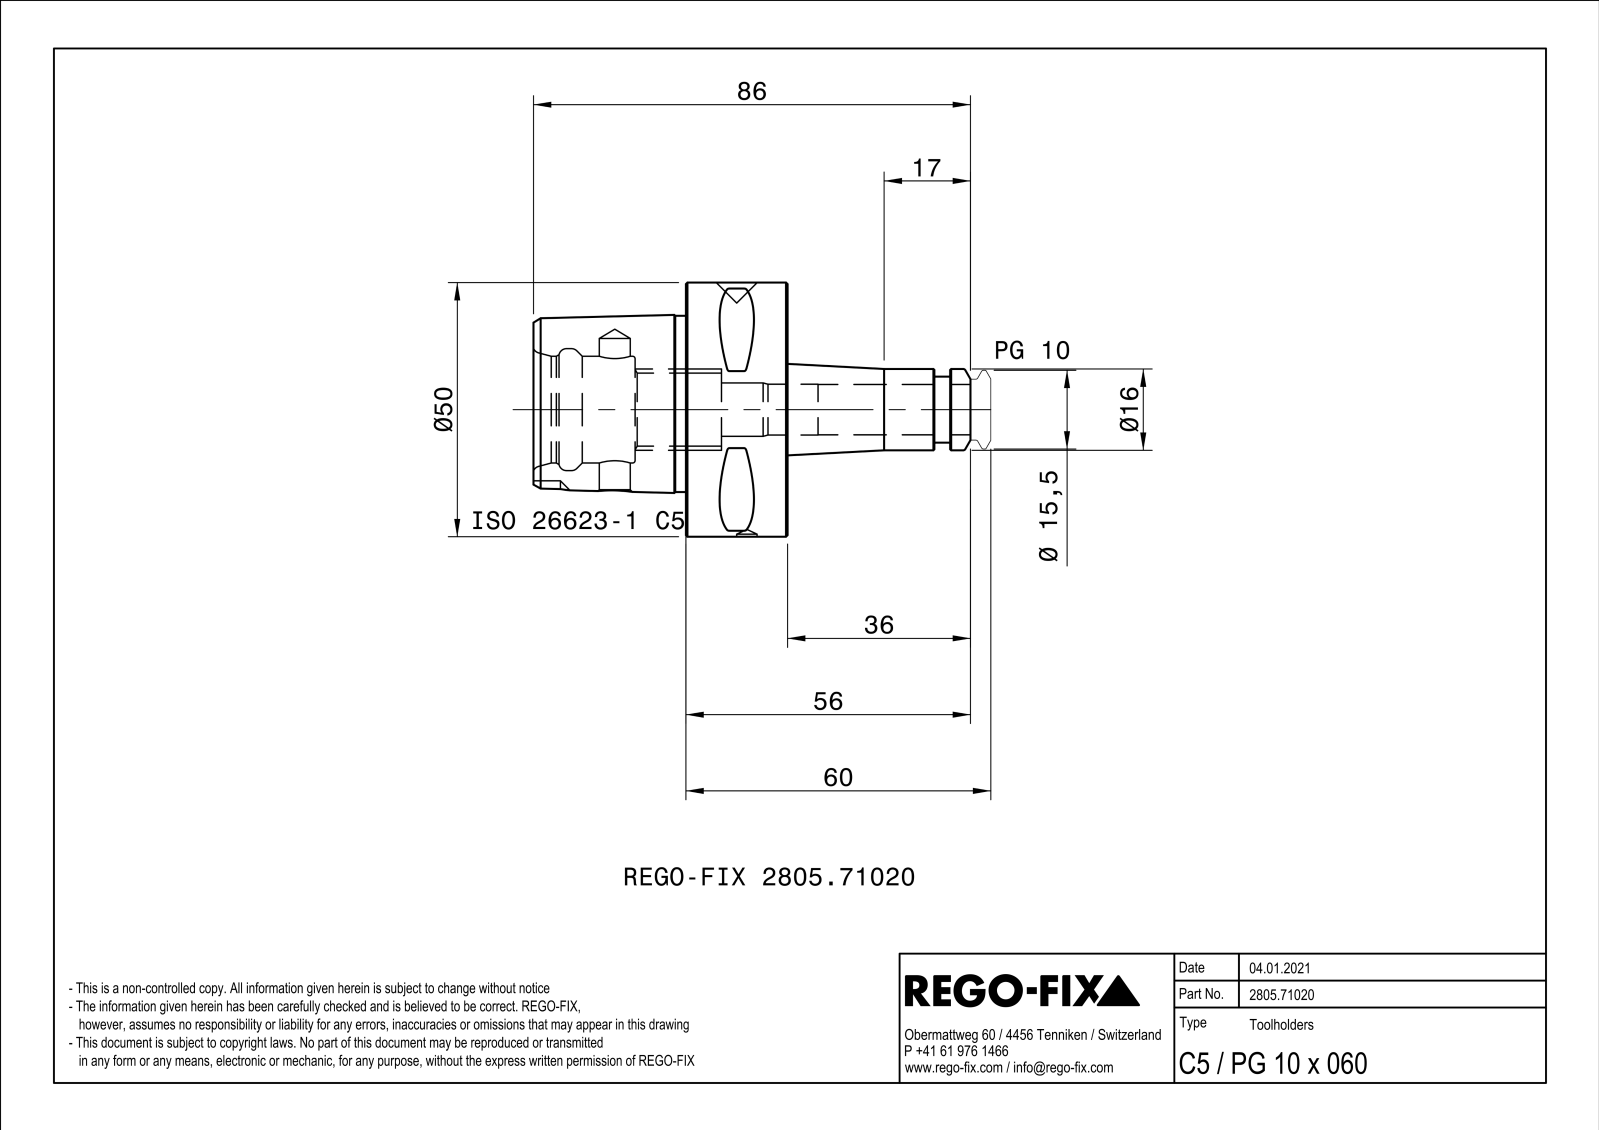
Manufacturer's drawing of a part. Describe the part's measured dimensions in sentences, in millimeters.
The part is named "NOCUT". Its 3-D file was written by "SIEMENS PLM Software Solid Edge ST10 (AUTOMOTIVE_DESIGN)". It is 1 solid with 113 faces: 23 planar, 22 cylindrical and 68 other. Overall it measures 80 by 40 by 40 millimeters. Its volume is 35 804 cubic millimeters and its surface area 11 912 square millimeters. Round holes: 1 of diameter 4, 1 of diameter 4.6, 1 of diameter 10, 1 of diameter 12.38, 1 of diameter 18, 1 of diameter 20. Round bosses or shafts: 1 of diameter 40, 1 of diameter 16, 1 of diameter 13. Partial cylindrical surfaces (rounded edges, fillets, slot ends): 8 of radius 0.5, 1 of radius 3. The main face-to-face distances are 20, 44, 24, 15.52, 29, 9, 15, 35.3, 3.1, 32. The hole center spacings are 23.5.
